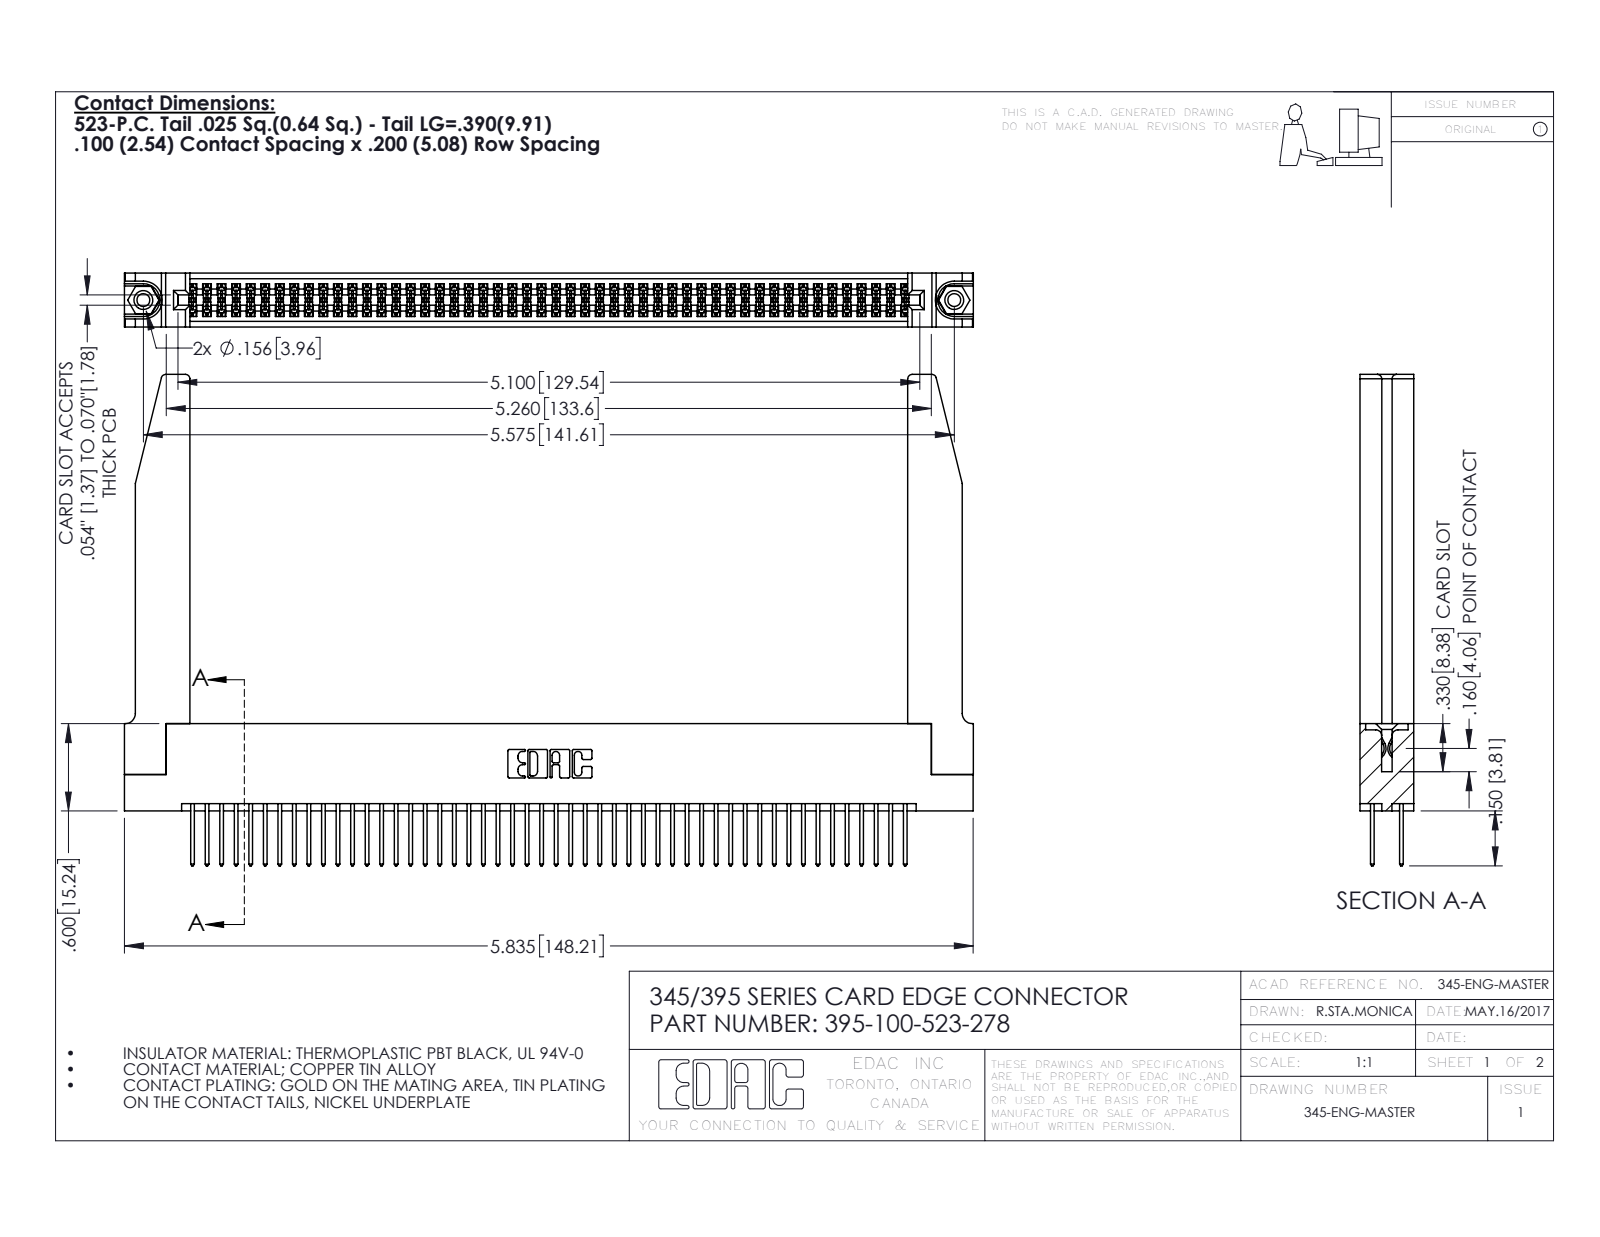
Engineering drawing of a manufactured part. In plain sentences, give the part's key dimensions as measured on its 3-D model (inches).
The part is named "345-292-001_345-293-123; 345 Part_Flush Mounting Lugs - 0.156 Dia-TH; 345-250-001_345-250-001-102; 395-100-523-278 (+1 more)". Its 3-D file was written by "SolidWorks 2016 (CONFIG_CONTROL_DESIGN)". It is 105 solids with 5360 faces: 3522 planar, 1786 cylindrical and 52 other. Overall it measures 5.836 by 3.377 by 0.37 inches. Its volume is 1.37 cubic inches and its surface area 45.9 square inches. Round holes: 2 of diameter 0.089, 2 of diameter 0.125, 2 of diameter 0.156, 1 of diameter 0.064. Round bosses or shafts: 2 of diameter 0.155. Partial cylindrical surfaces (rounded edges, fillets, slot ends): 150 of radius 0.006, 100 of radius 0.01, 22 of radius 0.01, 8 of radius 0.03, 6 of radius 0.007, 6 of radius 0.031, 3 of radius 0.026, 2 of radius 0.014. The main face-to-face distances are 0.072, 0.298, 0.37, 0.2, 0.098, 0.272, 0.025, 0.225, 0.175, 0.15. The hole center spacings are 0.27, 5.339, 5.575.
